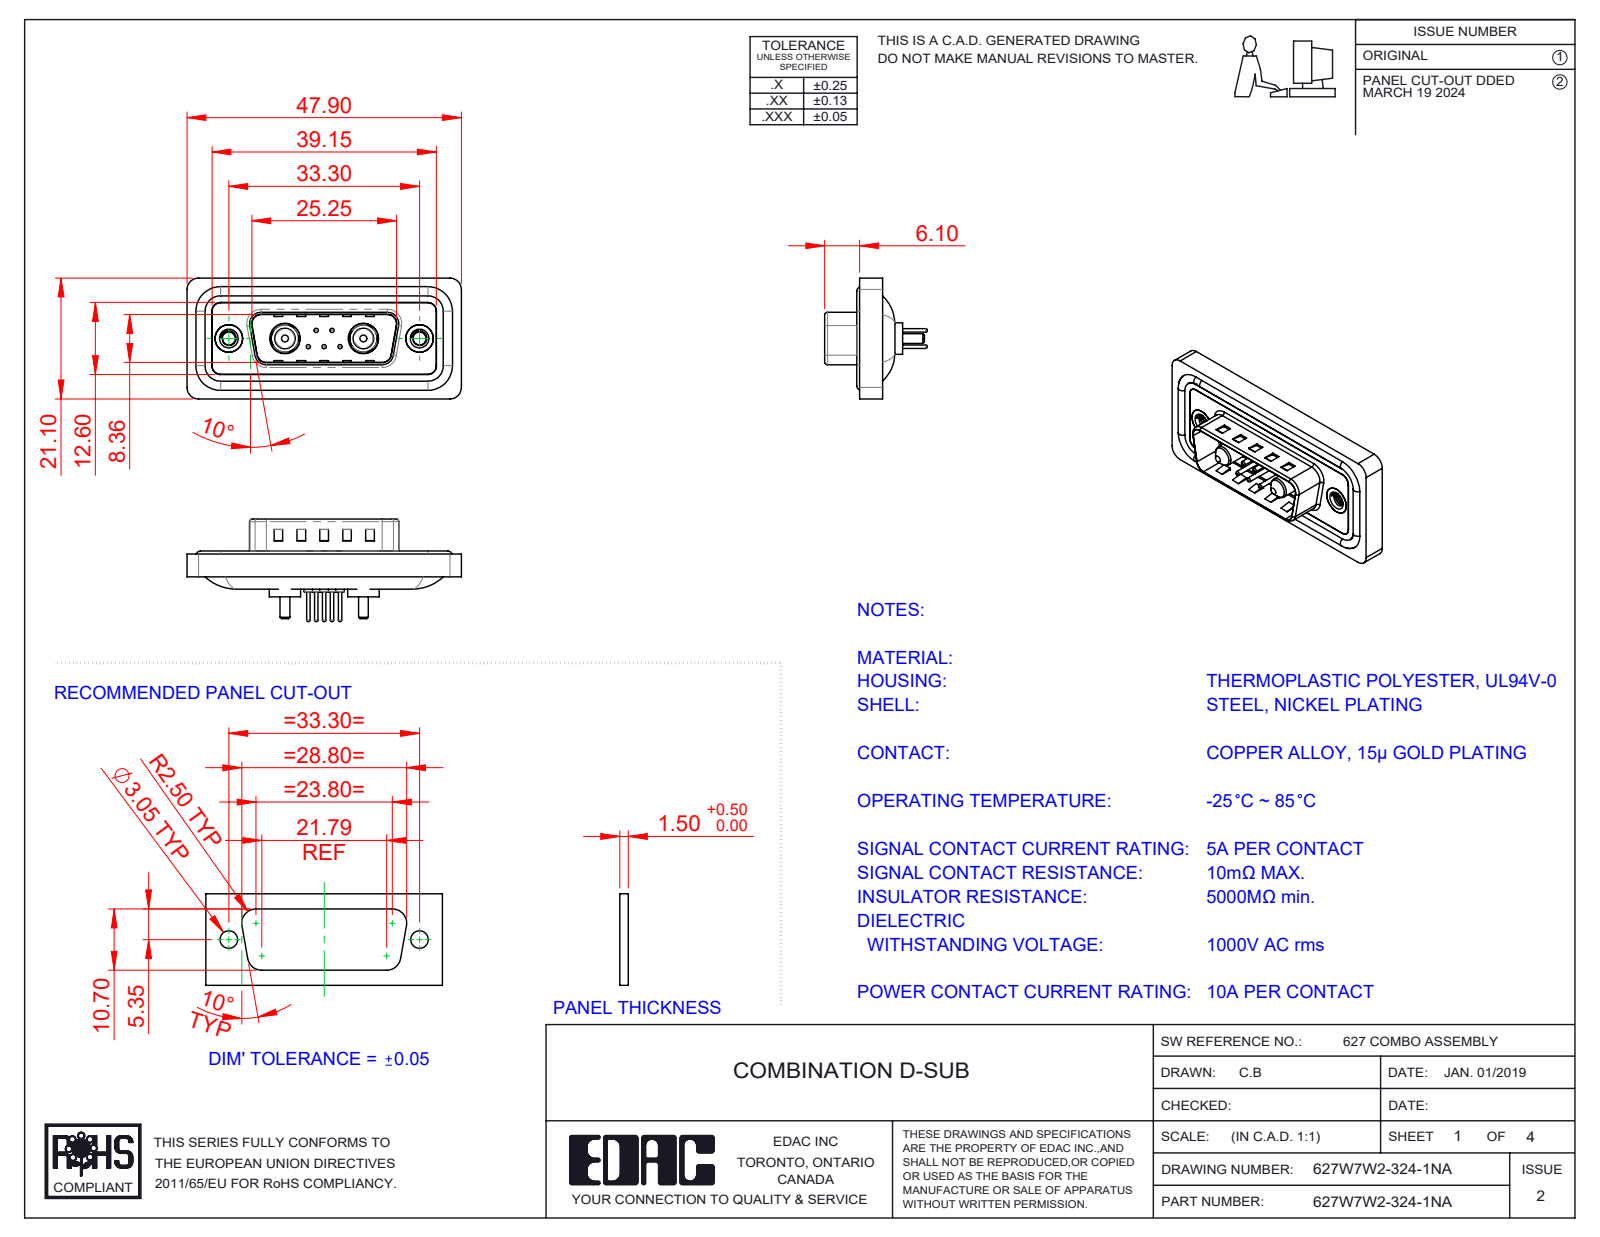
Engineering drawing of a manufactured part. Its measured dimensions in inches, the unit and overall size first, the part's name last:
Units: inches
Overall size (bounding box): 1.886 × 0.831 × 0.705
Round holes (diameter × count): ⌀0.03 ×5, ⌀0.063 ×5, ⌀0.079 ×5, ⌀0.089 ×2, ⌀0.157 ×2, ⌀0.189 ×2, ⌀0.191 ×2, ⌀0.197 ×2, ⌀0.209 ×2
Round bosses / shafts (diameter × count): ⌀0.059 ×5, ⌀0.024 ×5, ⌀0.063 ×4, ⌀0.217 ×2, ⌀0.205 ×2, ⌀0.193 ×2, ⌀0.187 ×2, ⌀0.148 ×2
Partial cylindrical surfaces — rounded edges, fillets, slot ends (radius × count): R0.059 ×26, R0.079 ×20, R0.02 ×8, R0.063 ×8, R0.01 ×4, R0.024 ×4, R0.026 ×4, R0.035 ×4
Main face-to-face distances: 0.016, 0.043, 0.059, 0.063, 0.02, 0.122, 0.114, 0.157, 0.032, 0.377
Hole centre spacings: 0.124, 0.109, 0.386, 0.925, 0.17, 0.17, 0.198, 0.198
Volume: 0.335 in³ · Surface area: 13.59 in²
Bodies: 16 solids, 708 faces (232 planar, 294 cylindrical, 182 other)
Part name (STEP PRODUCT): 627Combo Contact Row 2_24; 627Combo Housing_7W2; 627Combo Threaded Rivet_A; Power Pin_10A S (+5 more)
STEP written by: SolidWorks 2023 (CONFIG_CONTROL_DESIGN)
